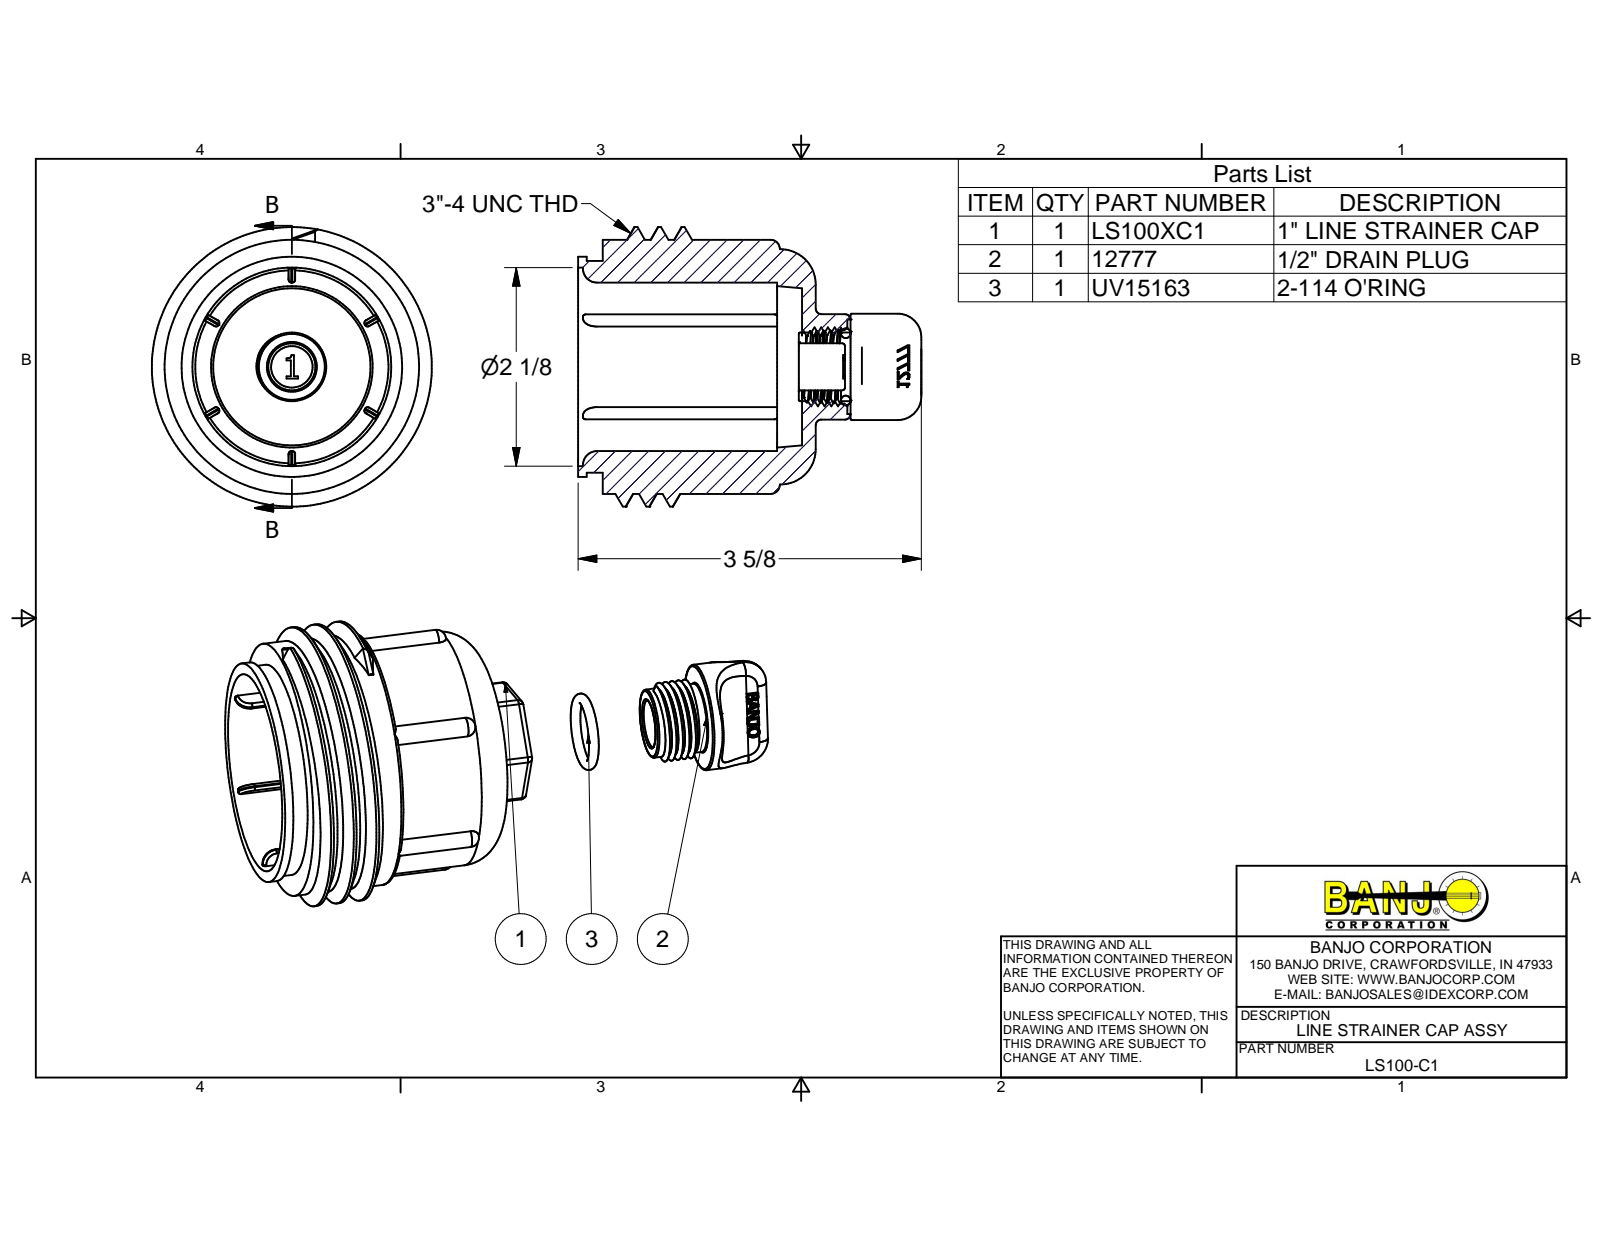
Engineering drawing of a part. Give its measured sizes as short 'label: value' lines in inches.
name: LS100-C1; LS100XC1; 12777; UV15163
written by: Autodesk Inventor 2013 (AUTOMOTIVE_DESIGN)
unit: in
bodies: 3 solids, 385 faces (174 planar, 74 cylindrical, 137 other)
size: 3.64 × 2.971 × 2.971
volume: 6.082 in³; area: 64.27 in²
holes: 1× ⌀0.5, 1× ⌀1.005, 1× ⌀2.11
bosses: 1× ⌀2.971, 1× ⌀2.7, 1× ⌀2.5, 1× ⌀2.34, 1× ⌀2.25, 1× ⌀1.13, 1× ⌀0.73
rounds: 18× R0.03, 18× R0.06, 6× R0.1, 6× R0.15, 2× R0.38
face distances: 2.115, 0.07, 0.145, 2.26, 1.85, 0.265, 0.41, 0.26, 2.11, 2.375
